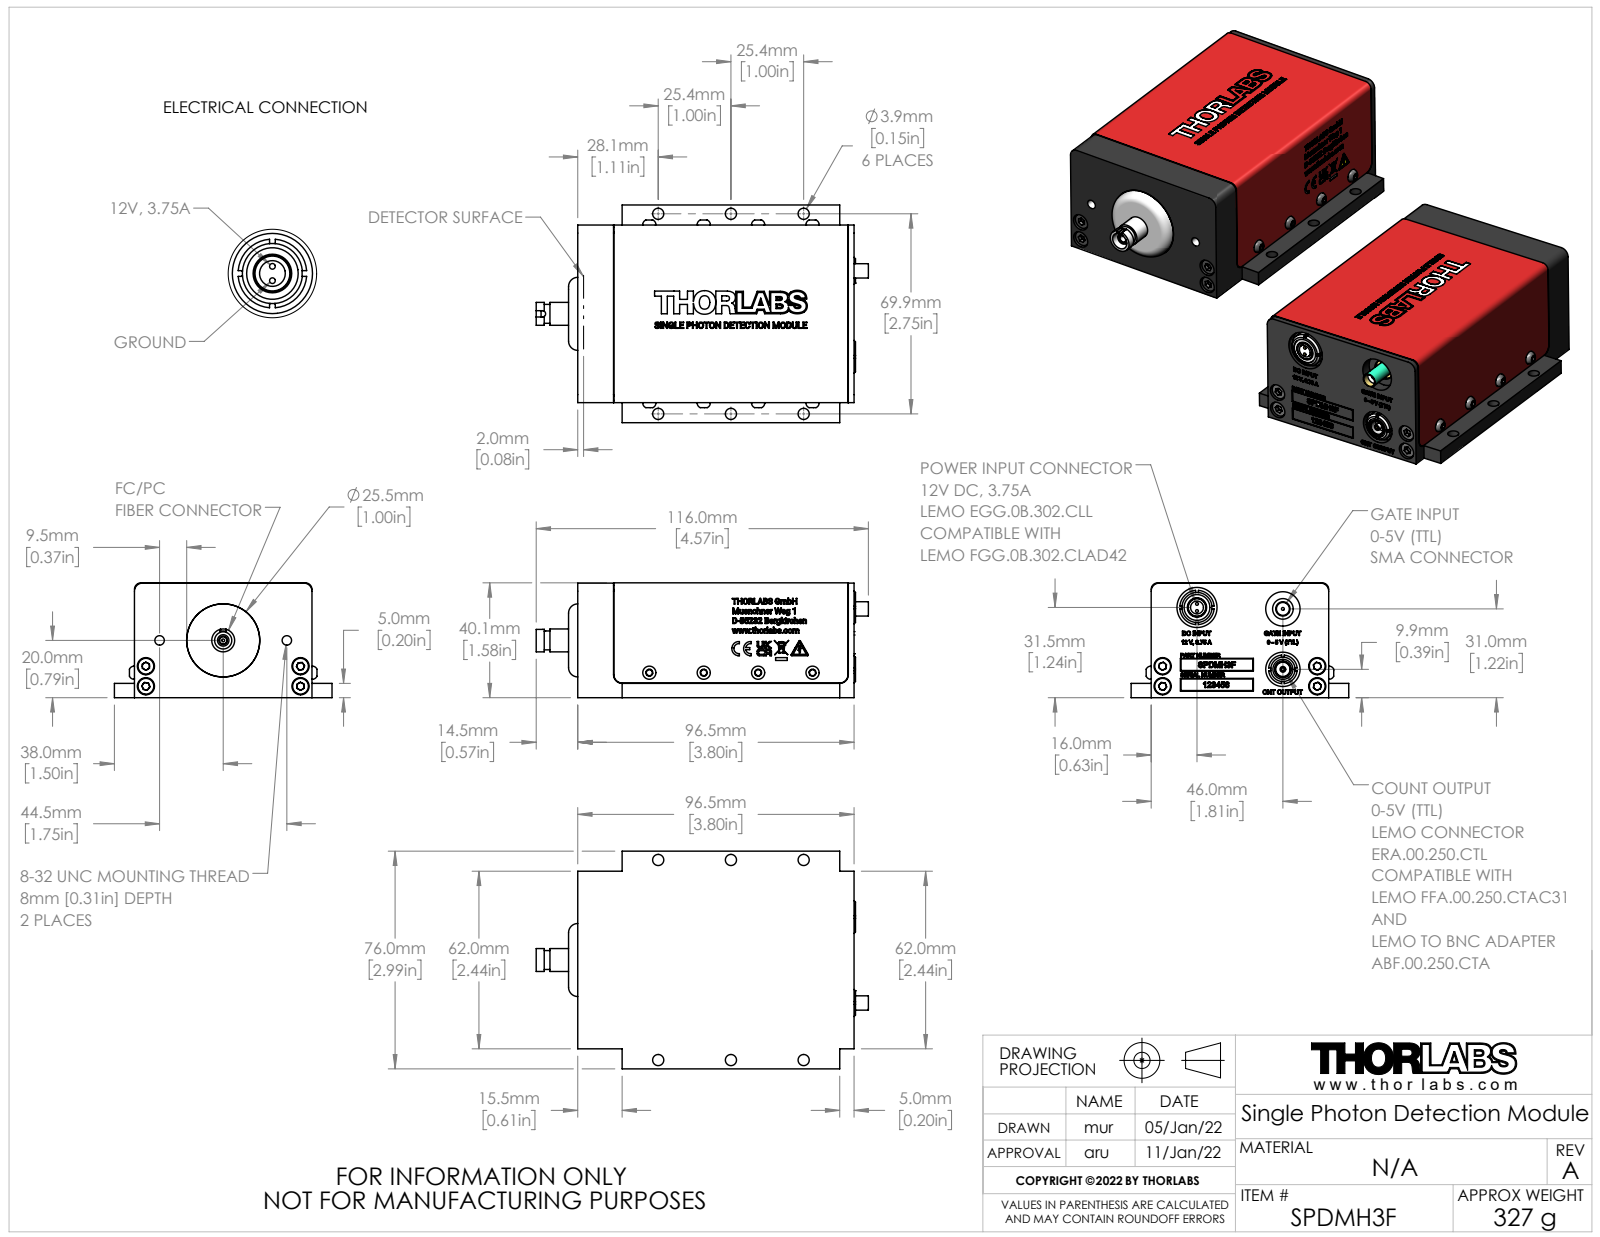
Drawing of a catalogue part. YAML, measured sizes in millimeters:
part_name: "22.02.08_SPDMH3F WEB"
step_written_by: "SolidWorks 2019 (AUTOMOTIVE_DESIGN)"
units: millimeters
bodies: {solids: 2, faces: 2711, planar: 1949, cylindrical: 224, other: 538}
overall_size: [116.01, 76, 40.1]
volume: 94150
surface_area: 54058
round_holes:
  - {diameter: 3.9, count: 6}
  - {diameter: 1, count: 5}
  - {diameter: 6, count: 5}
  - {diameter: 2.01, count: 4}
  - {diameter: 2.2, count: 4}
  - {diameter: 2.46, count: 4}
  - {diameter: 3.2, count: 4}
  - {diameter: 4.3, count: 4}
  - {diameter: 1.98, count: 2}
  - {diameter: 2, count: 2}
  - {diameter: 3.31, count: 2}
  - {diameter: 7.2, count: 2}
round_bosses_or_shafts:
  - {diameter: 5.5, count: 4}
  - {diameter: 3, count: 4}
  - {diameter: 13.97, count: 1}
  - {diameter: 12, count: 1}
  - {diameter: 10, count: 1}
  - {diameter: 9.1, count: 1}
  - {diameter: 9, count: 1}
  - {diameter: 8, count: 1}
partial_cylinders:
  - {radius: 0.21, count: 6}
  - {radius: 0.73, count: 6}
  - {radius: 1.25, count: 4}
  - {radius: 1.4, count: 4}
  - {radius: 3, count: 4}
  - {radius: 0.16, count: 3}
  - {radius: 0.3, count: 3}
  - {radius: 0.84, count: 3}
face_to_face_distances: [0.8, 5, 39.3, 34.3, 40.1, 35.1, 62, 61.2, 76, 15.5]
hole_center_spacings: [19, 25.4, 9.5, 13.44, 24.17, 24.52, 29.21, 46]
